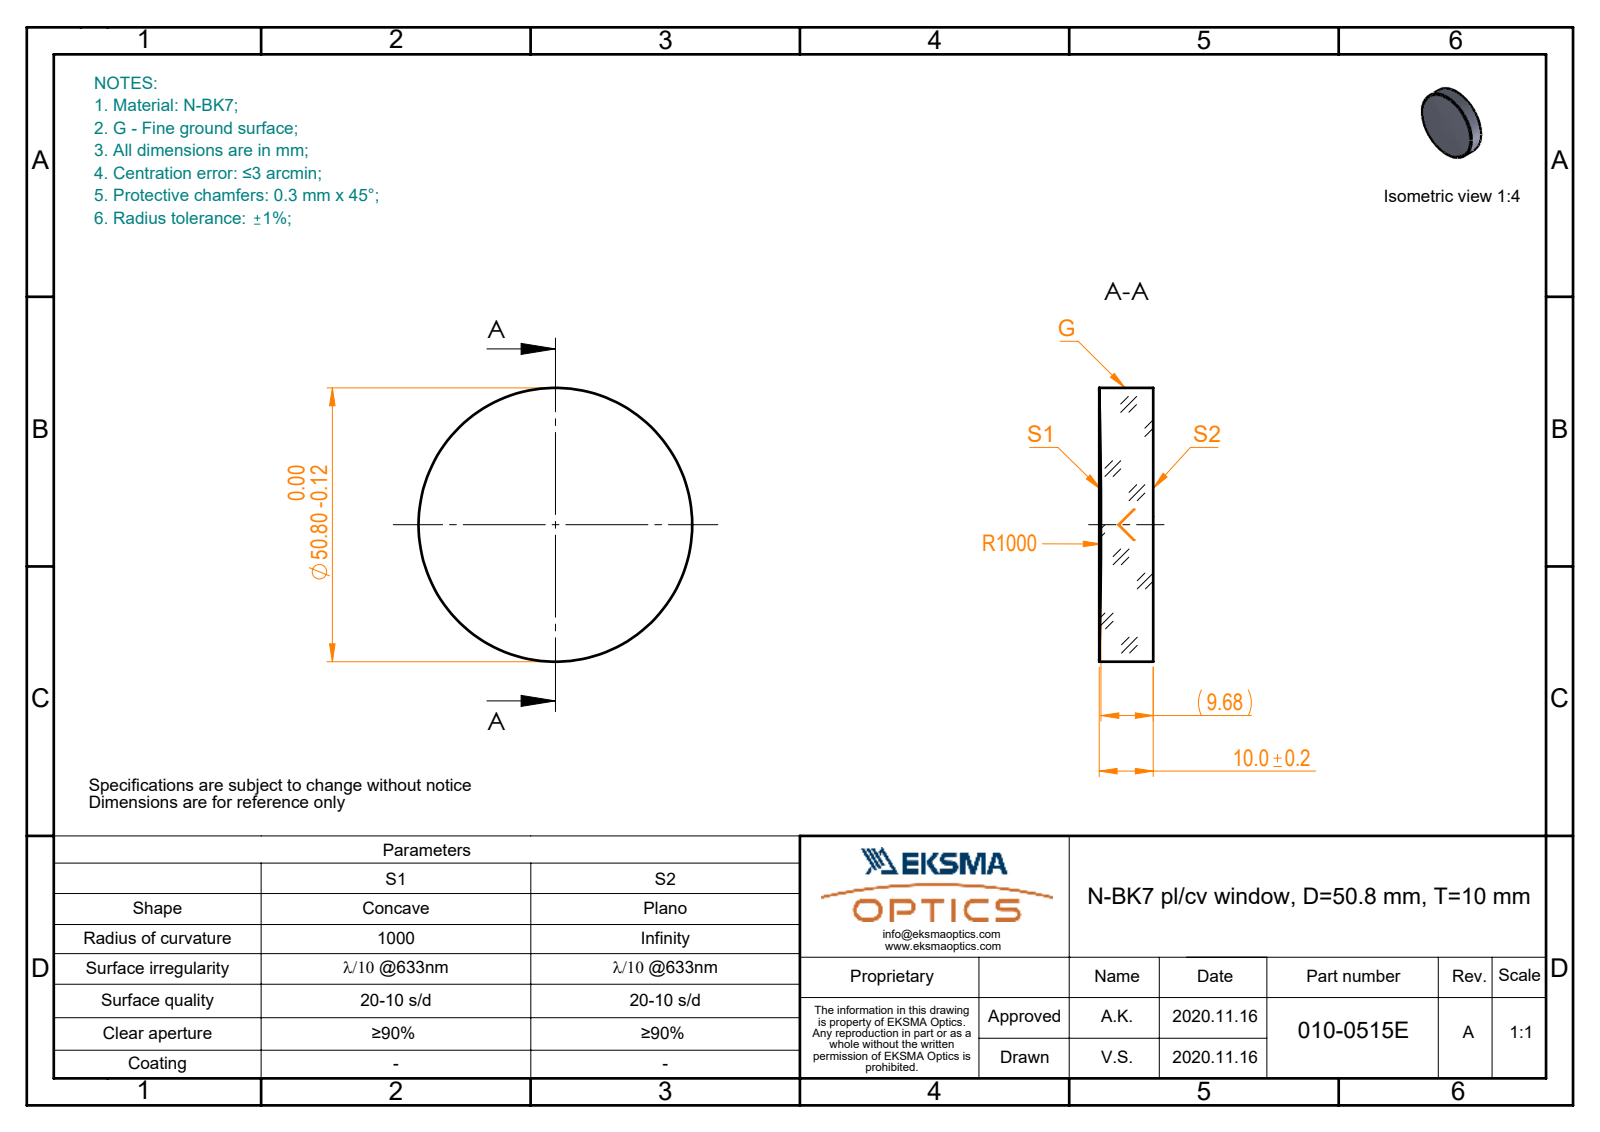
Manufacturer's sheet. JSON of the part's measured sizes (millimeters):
{"part_name": "010-0515E_N-BK7_PCV_window", "step_written_by": "SolidWorks 2019 (CONFIG_CONTROL_DESIGN)", "units": "millimeters", "bodies": {"solids": 1, "faces": 5, "planar": 1, "cylindrical": 2, "other": 2}, "overall_size": [50.8, 50.8, 10], "volume_mm3": 19941, "surface_area_mm2": 5650, "round_bosses_or_shafts": [[50.8, 1]]}
